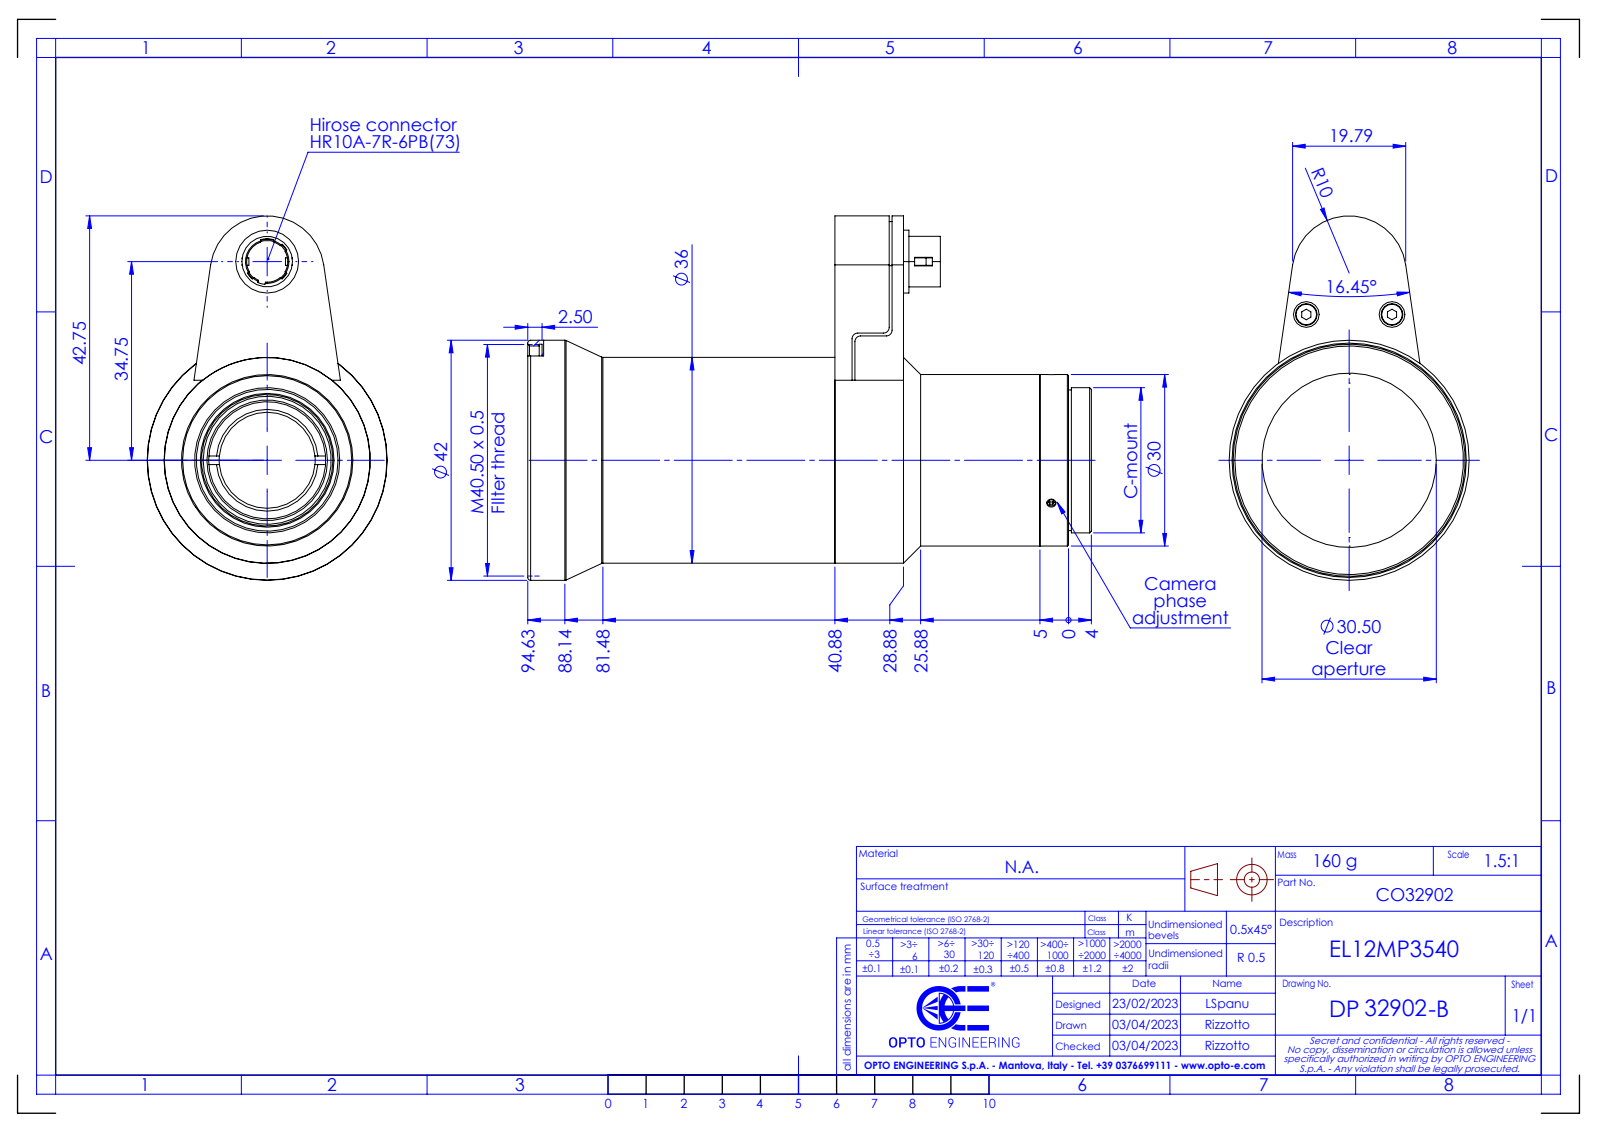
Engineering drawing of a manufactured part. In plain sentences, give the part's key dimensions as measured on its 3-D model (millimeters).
The part is named "DP32902-B_EL12MP3540". Its 3-D file was written by "SolidWorks 2021 (CONFIG_CONTROL_DESIGN)". It is 0 solids with 110 faces: 31 planar, 56 cylindrical and 23 other. Overall it measures 98.63 by 63.75 by 42 millimeters. Round holes: 2 of diameter 1.6, 1 of diameter 7.4, 1 of diameter 16.8, 1 of diameter 20.5, 1 of diameter 23, 1 of diameter 30.5, 1 of diameter 40. Round bosses or shafts: 1 of diameter 42, 1 of diameter 36, 1 of diameter 30, 1 of diameter 25.4, 1 of diameter 24.6, 1 of diameter 11, 1 of diameter 8.85. Partial cylindrical surfaces (rounded edges, fillets, slot ends): 2 of radius 1, 1 of radius 3.6, 1 of radius 3.9, 1 of radius 4, 1 of radius 10. The main face-to-face distances are 1, 63.25, 51.25, 50.25, 62.25, 12, 40.88, 92.13, 91.13, 28.88. The hole center spacings are 34.75.
